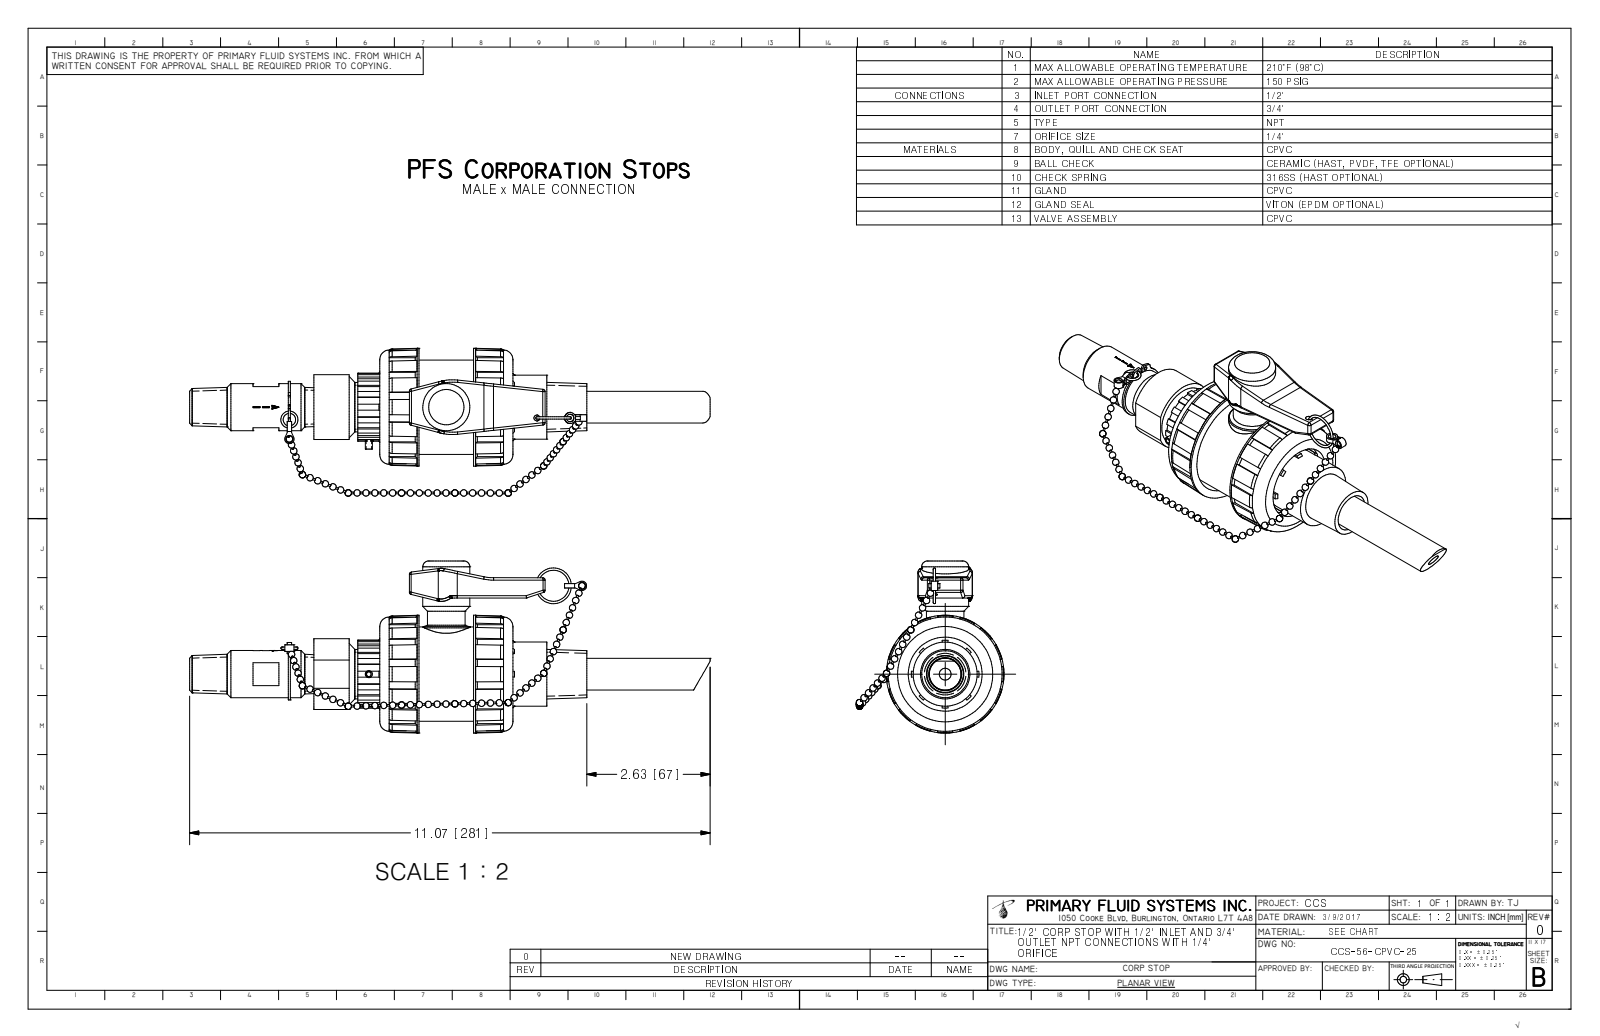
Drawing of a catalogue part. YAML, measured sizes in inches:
part_name: "CCS-56-CPVC-25_R0"
step_written_by: "Autodesk Inventor 2009 (AUTOMOTIVE_DESIGN)"
units: inches
bodies: {solids: 1, faces: 605, planar: 225, cylindrical: 146, other: 234}
overall_size: [11.069, 3.65, 3.139]
volume: 18.42
surface_area: 104.9
round_holes:
  - {diameter: 0.079, count: 1}
  - {diameter: 0.25, count: 1}
  - {diameter: 0.469, count: 1}
  - {diameter: 0.56, count: 1}
  - {diameter: 1.57, count: 1}
  - {diameter: 2.16, count: 1}
round_bosses_or_shafts:
  - {diameter: 1, count: 2}
  - {diameter: 2.5, count: 1}
  - {diameter: 2, count: 1}
  - {diameter: 1.801, count: 1}
  - {diameter: 1.36, count: 1}
  - {diameter: 1.094, count: 1}
  - {diameter: 0.8, count: 1}
  - {diameter: 0.675, count: 1}
partial_cylinders:
  - {radius: 0.05, count: 21}
  - {radius: 1, count: 3}
  - {radius: 0.043, count: 2}
  - {radius: 0.157, count: 2}
  - {radius: 0.351, count: 1}
  - {radius: 0.457, count: 1}
  - {radius: 0.463, count: 1}
  - {radius: 0.499, count: 1}
face_to_face_distances: [0.205, 2.625, 0.835, 1.995, 0.63, 1.79, 0.465, 2.83, 2.42, 1.16]
hole_center_spacings: [0.563]
